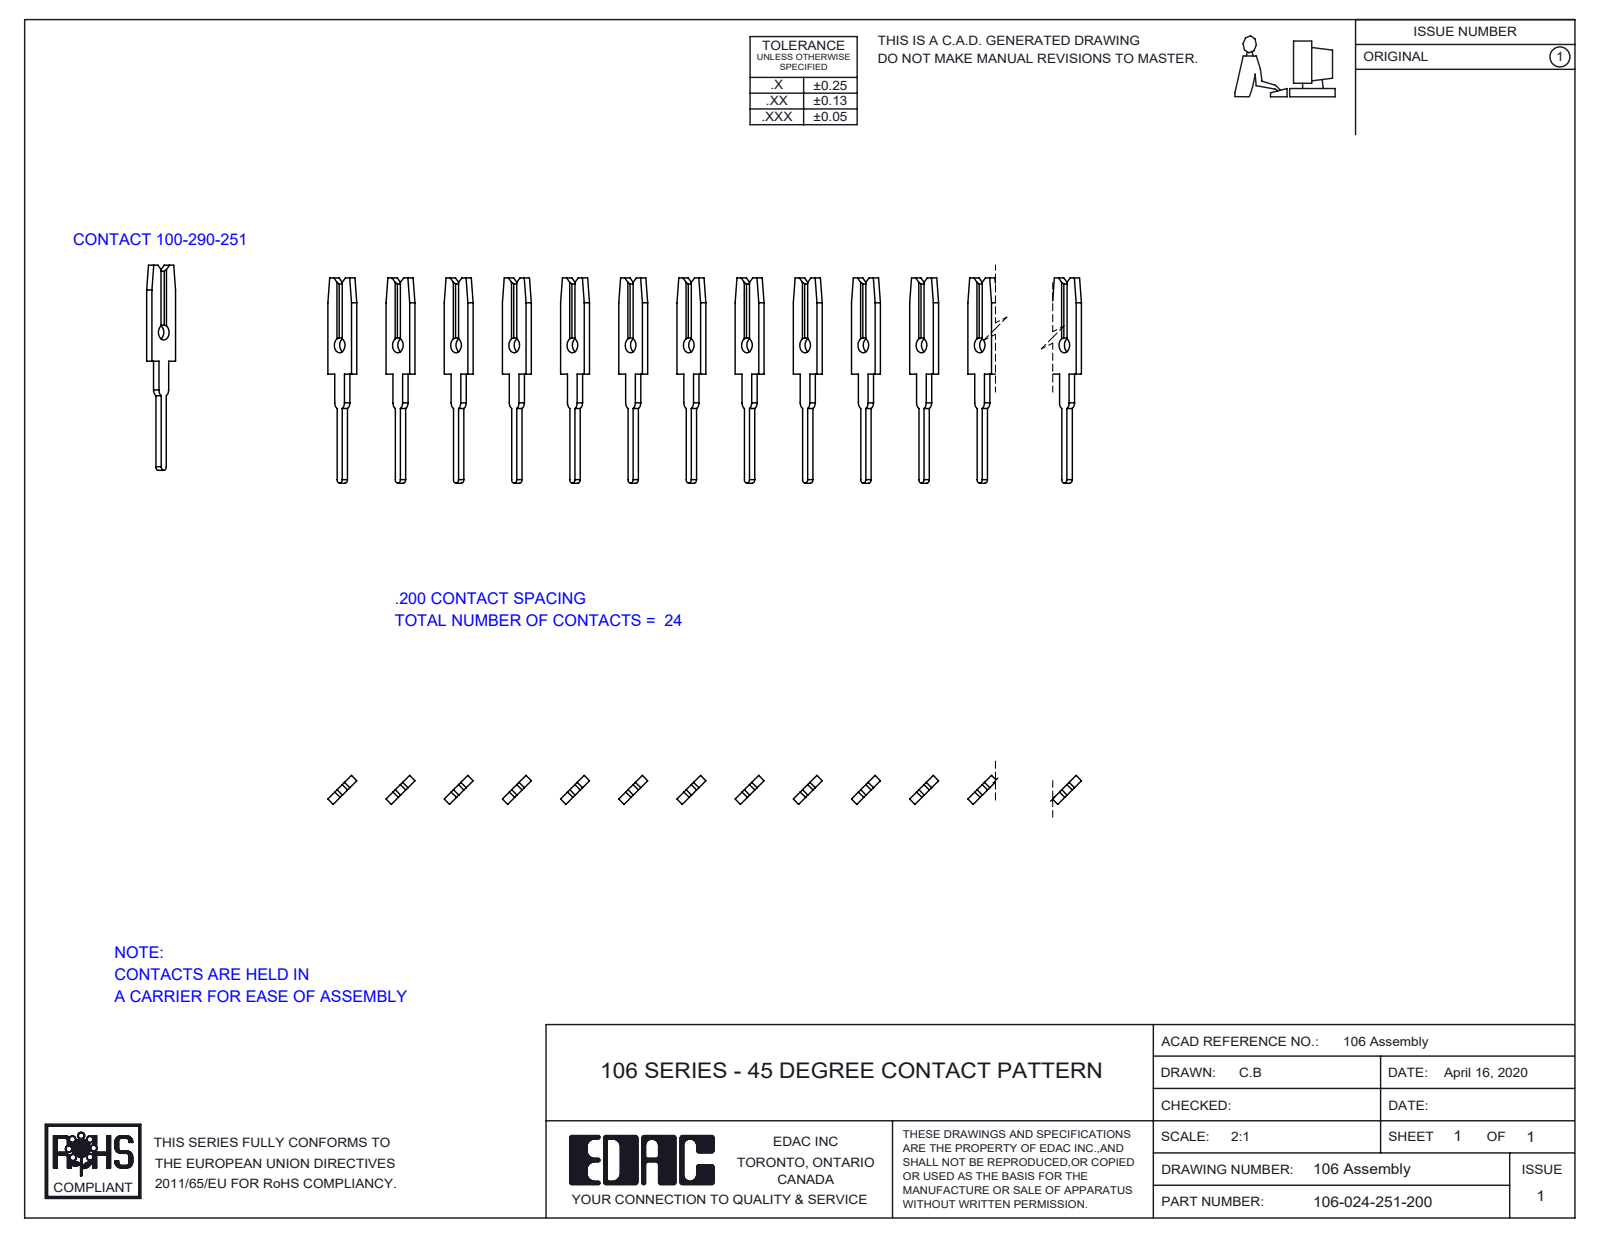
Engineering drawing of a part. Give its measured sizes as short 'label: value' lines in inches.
name: 106-024-251-200; 100-290-001_100-290-251
written by: SolidWorks 2016 (CONFIG_CONTROL_DESIGN)
unit: in
bodies: 24 solids, 672 faces (528 planar, 144 cylindrical, 0 other)
size: 4.7 × 0.705 × 0.1
volume: 0.027 in³; area: 3.343 in²
holes: 24× ⌀0.052
rounds: 24× R0.012, 24× R0.024
face distances: 0.141, 0.848, 0.283, 0.707, 0.99, 0.566, 1.131, 0.424, 0.424, 1.556
hole spacings: 0.141, 0.283, 0.424, 1.131, 0.848, 1.556, 1.697, 1.839
